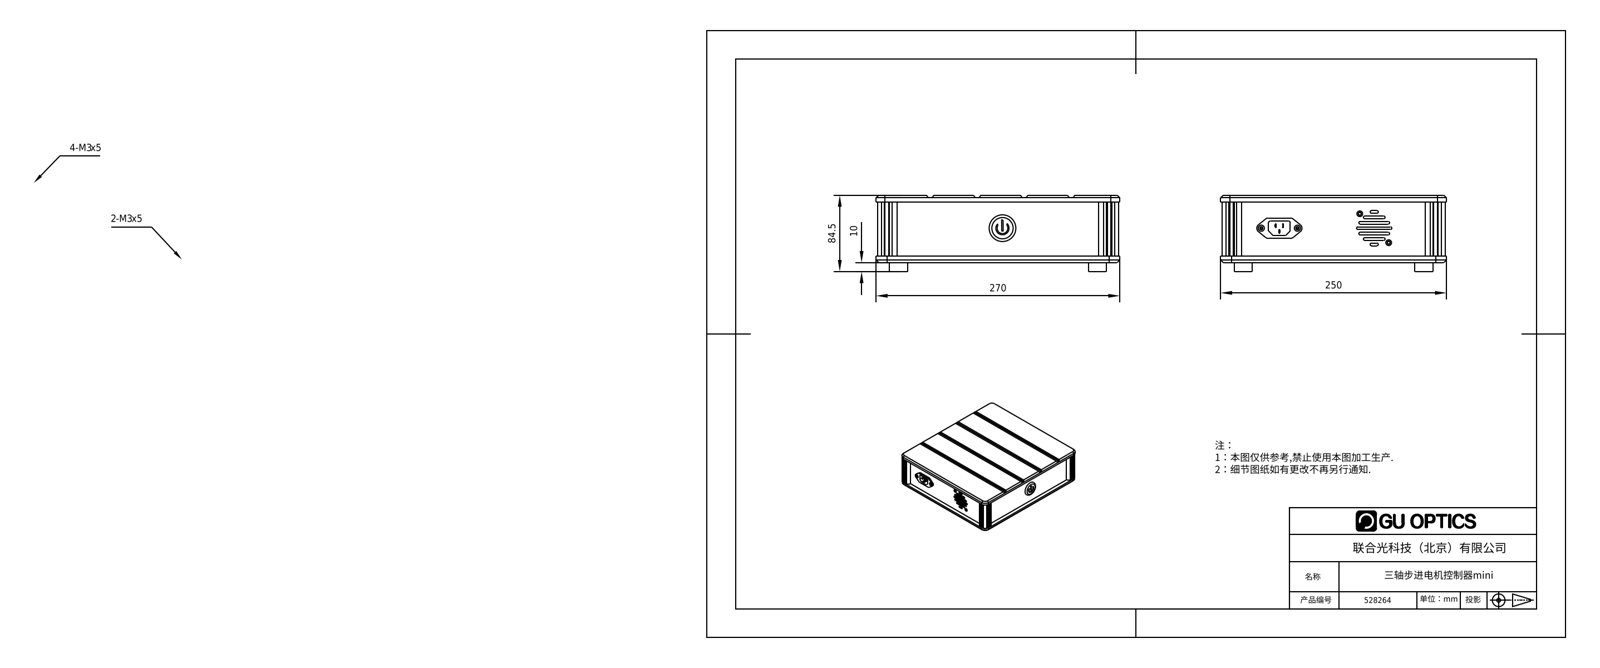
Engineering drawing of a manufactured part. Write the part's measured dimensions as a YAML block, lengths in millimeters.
part_name: "528264"
step_written_by: "SolidWorks 2020 (CONFIG_CONTROL_DESIGN)"
units: millimeters
bodies: {solids: 93, faces: 5842, planar: 3377, cylindrical: 1401, other: 1064}
overall_size: [270, 250, 84.5]
volume: 2659000
surface_area: 762155
round_holes:
  - {diameter: 1, count: 66}
  - {diameter: 1.1, count: 66}
  - {diameter: 2.5, count: 61}
  - {diameter: 3.2, count: 30}
  - {diameter: 2.05, count: 16}
  - {diameter: 3.3, count: 14}
  - {diameter: 3.5, count: 14}
  - {diameter: 3.4, count: 9}
  - {diameter: 4.5, count: 8}
  - {diameter: 8, count: 8}
  - {diameter: 4.75, count: 6}
  - {diameter: 2.46, count: 2}
round_bosses_or_shafts:
  - {diameter: 1.5, count: 66}
  - {diameter: 3, count: 34}
  - {diameter: 5.5, count: 18}
  - {diameter: 7, count: 8}
  - {diameter: 4, count: 8}
  - {diameter: 20, count: 4}
  - {diameter: 5.54, count: 4}
  - {diameter: 6.4, count: 3}
partial_cylinders:
  - {radius: 0.5, count: 259}
  - {radius: 1, count: 117}
  - {radius: 1.5, count: 42}
  - {radius: 0.3, count: 36}
  - {radius: 2.5, count: 28}
  - {radius: 0.2, count: 27}
  - {radius: 0.92, count: 24}
  - {radius: 1, count: 24}
face_to_face_distances: [7, 67, 60, 7.5, 74.5, 67.5, 3, 5, 30, 9.2]
hole_center_spacings: [3.16, 2.77, 5.54, 8.31, 5.03, 5.04, 11.08, 7.48]
